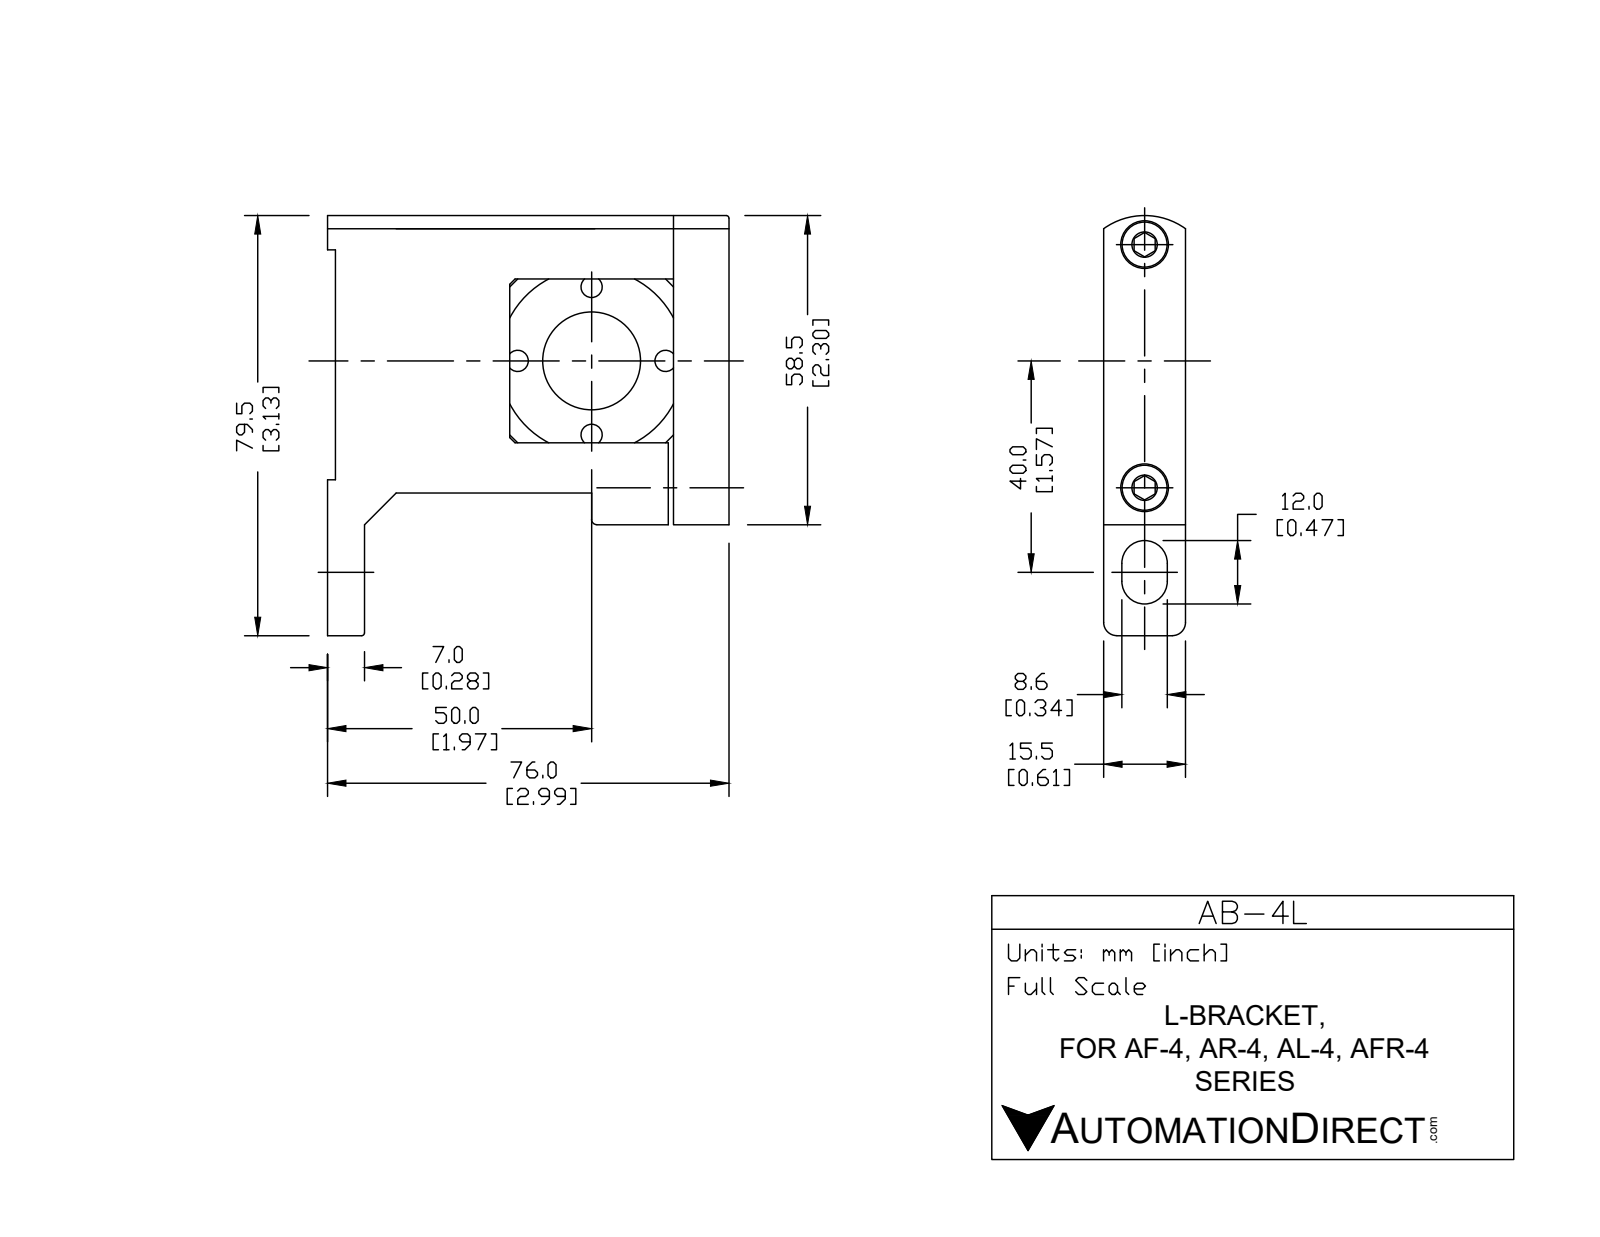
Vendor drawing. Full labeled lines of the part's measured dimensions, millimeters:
Part name (STEP PRODUCT): AB-4L
STEP written by: SolidWorks 2015 (CONFIG_CONTROL_DESIGN)
Units: millimetres
Bodies: 3 solids, 103 faces (69 planar, 22 cylindrical, 12 other)
Overall size (bounding box): 79.5 × 76 × 15.5
Volume: 48 404 mm³ · Surface area: 17 522 mm²
Round holes (diameter × count): ⌀5.5 ×2, ⌀8.37 ×2, ⌀18.5 ×1
Round bosses / shafts (diameter × count): ⌀7.75 ×2, ⌀4 ×2
Partial cylindrical surfaces — rounded edges, fillets, slot ends (radius × count): R4.3 ×2, R1.5 ×1, R13.26 ×1
Main face-to-face distances: 15.5, 2.5, 33.5, 74.25, 7, 2.75, 12.75, 7.19, 8.31, 4.44
Hole centre spacings: 46
